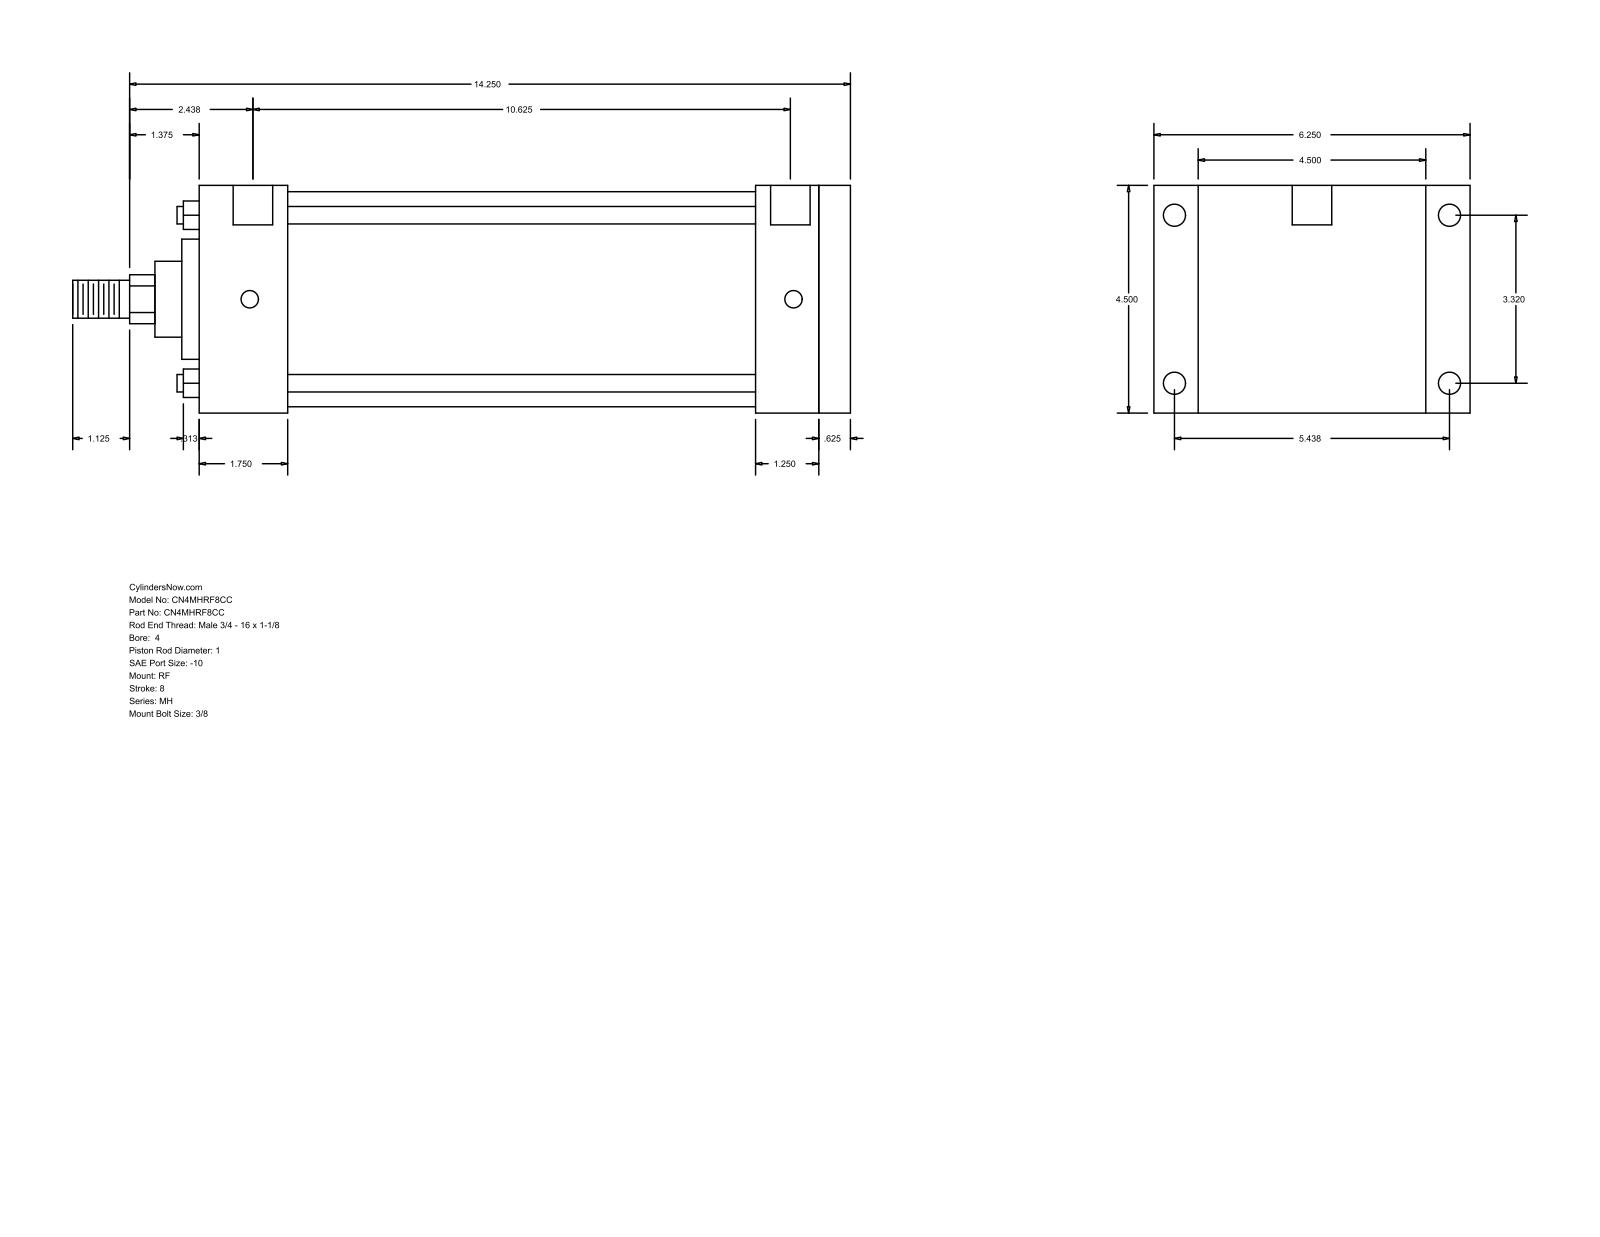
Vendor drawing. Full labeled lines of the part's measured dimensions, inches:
Part name (STEP PRODUCT): MH_RF__0400_1
STEP written by: GSSL Pune (CONFIG_CONTROL_DESIGN)
Units: inches
Bodies: 0 solids, 94 faces (65 planar, 29 cylindrical, 0 other)
Overall size (bounding box): 15.375 × 6.25 × 4.5
Round holes (diameter × count): ⌀0.344 ×4, ⌀0.438 ×4, ⌀0.781 ×2
Round bosses / shafts (diameter × count): ⌀0.345 ×4, ⌀4.25 ×1, ⌀2.375 ×1, ⌀1.5 ×1, ⌀1 ×1, ⌀0.75 ×1
Partial cylindrical surfaces — rounded edges, fillets, slot ends (radius × count): R0.484 ×1
Main face-to-face distances: 4.5, 12.875, 12.25, 0.625, 1.875, 1.75, 10.5, 11.125, 11, 9.25
Hole centre spacings: 3.32, 5.438, 6.371, 10.75, 0.062, 0.063, 10.625, 10.687
